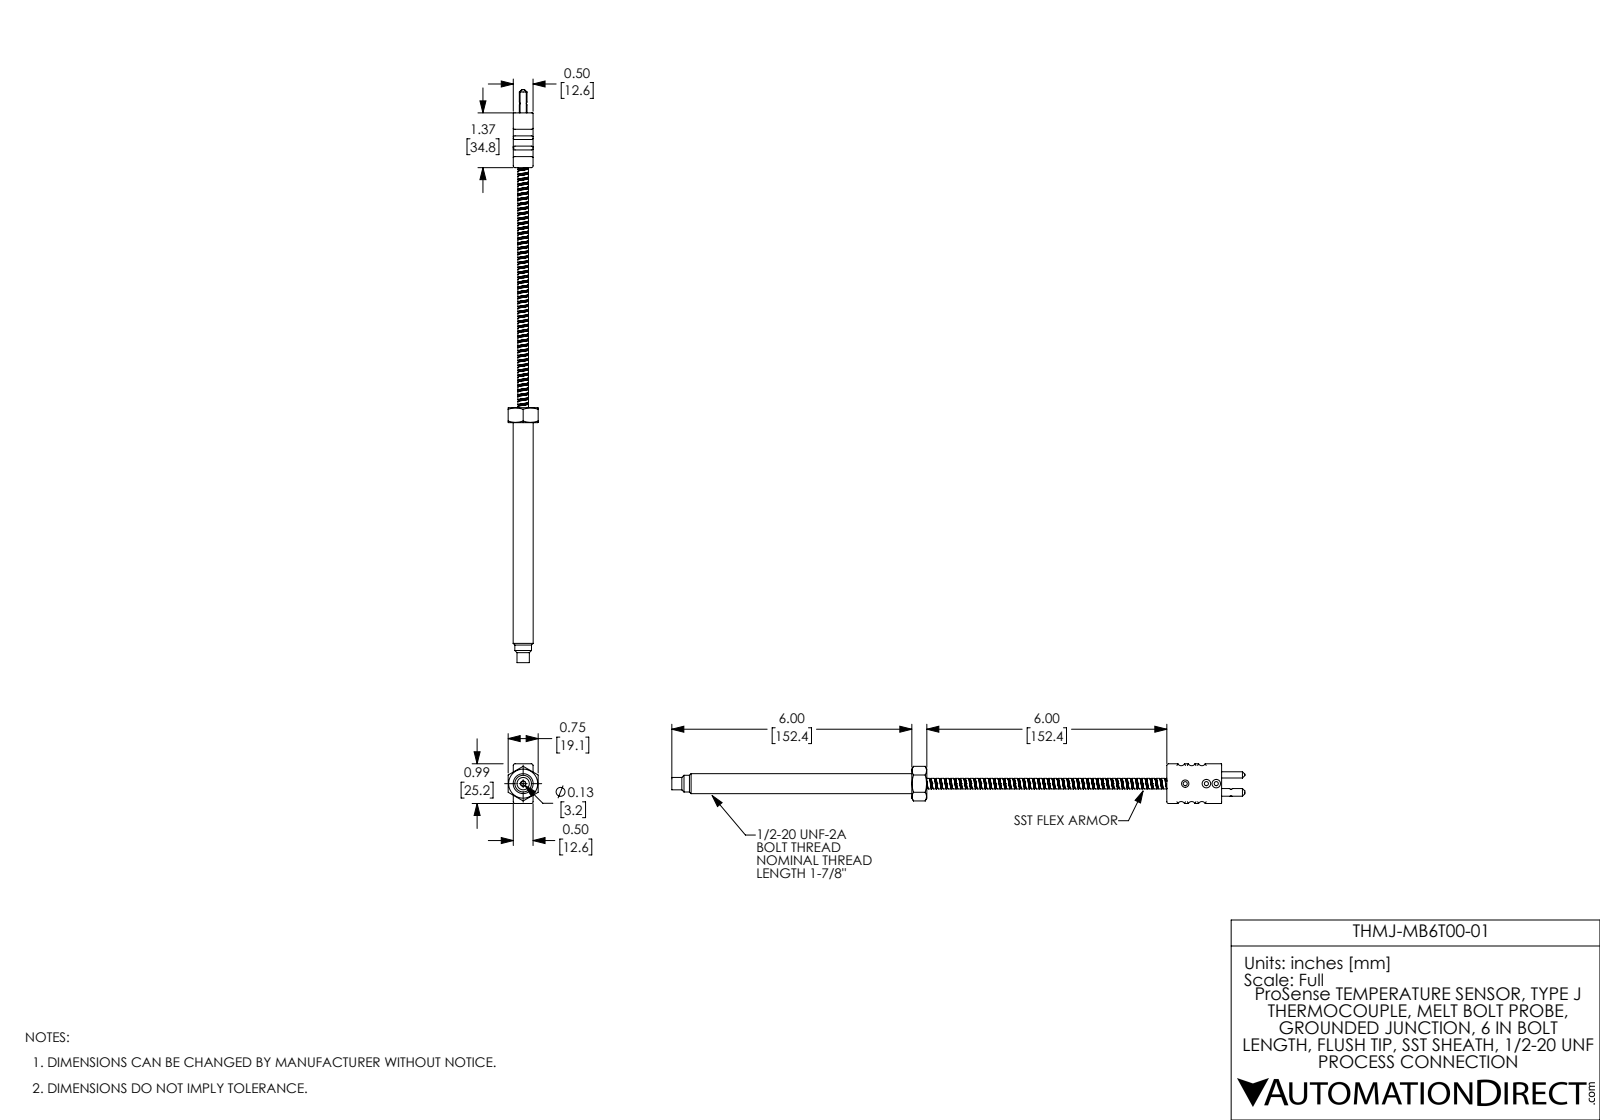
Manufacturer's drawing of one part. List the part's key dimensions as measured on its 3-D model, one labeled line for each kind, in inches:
Part name (STEP PRODUCT): THMJ-MB6T00-01
STEP written by: SolidWorks 2017 (AUTOMOTIVE_DESIGN)
Units: inches
Bodies: 3 solids, 312 faces (69 planar, 172 cylindrical, 71 other)
Overall size (bounding box): 14.326 × 0.993 × 0.75
Volume: 2.271 in³ · Surface area: 23.83 in²
Round holes (diameter × count): ⌀0.103 ×2, ⌀0.158 ×2, ⌀0.135 ×1, ⌀0.185 ×1, ⌀0.294 ×1, ⌀0.308 ×1
Round bosses / shafts (diameter × count): ⌀0.5 ×1, ⌀0.417 ×1, ⌀0.309 ×1, ⌀0.278 ×1, ⌀0.265 ×1, ⌀0.191 ×1, ⌀0.156 ×1, ⌀0.125 ×1
Partial cylindrical surfaces — rounded edges, fillets, slot ends (radius × count): R0.045 ×8, R0.095 ×6, R0.01 ×4
Main face-to-face distances: 0.495, 0.75, 7.369, 6, 0.993, 0.127, 0.622, 1.369, 6.375, 7.744
Hole centre spacings: 0.217, 0.328, 0.572, 0.247, 0.433, 0.529, 0.776
